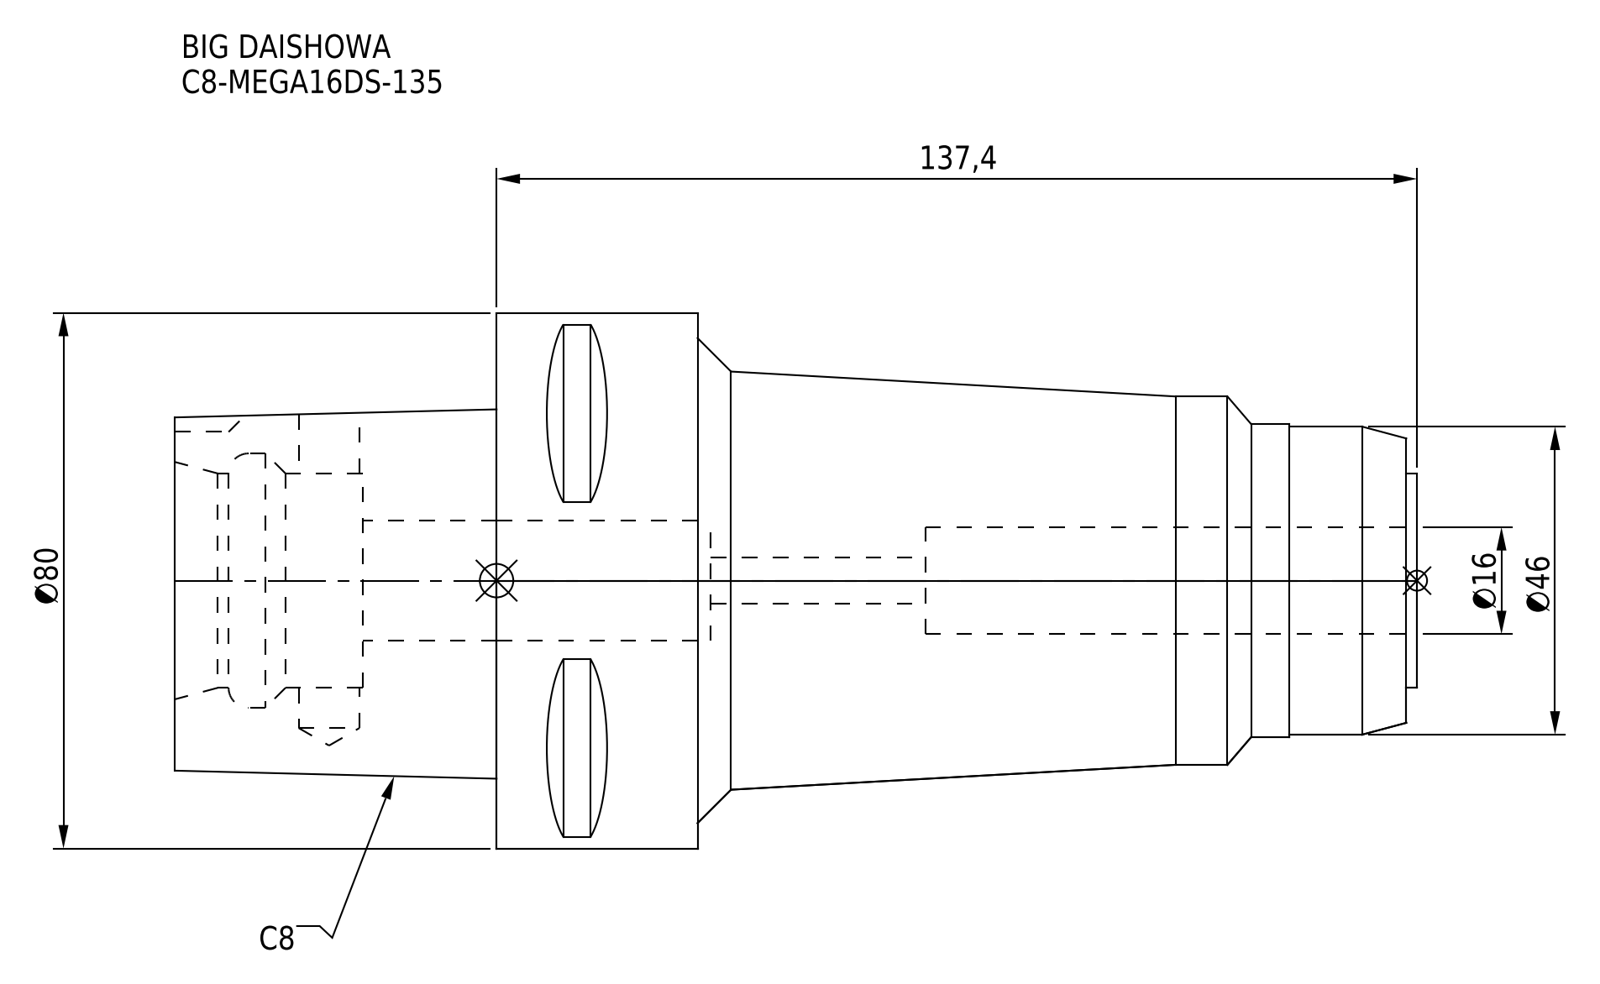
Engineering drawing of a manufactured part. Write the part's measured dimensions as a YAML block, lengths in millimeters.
part_name: "C8-MEGA16DS-135"
step_written_by: "CREO PARAMETRIC BY PTC INC, 2016380 (AUTOMOTIVE_DESIGN)"
units: millimeters
bodies: {solids: 1, faces: 76, planar: 31, cylindrical: 27, other: 18}
overall_size: [185.4, 80, 80]
volume: 463590
surface_area: 53584
round_holes:
  - {diameter: 6.8, count: 1}
  - {diameter: 9.1, count: 1}
  - {diameter: 16, count: 1}
  - {diameter: 18, count: 1}
  - {diameter: 32, count: 1}
  - {diameter: 38, count: 1}
round_bosses_or_shafts:
  - {diameter: 80, count: 1}
  - {diameter: 55, count: 1}
  - {diameter: 46.7, count: 1}
  - {diameter: 46, count: 1}
  - {diameter: 31.9, count: 1}
partial_cylinders:
  - {radius: 6, count: 1}
face_to_face_distances: [48, 30, 78, 105.8, 135.8, 183.8, 1.6, 107.4, 137.4, 185.4]
